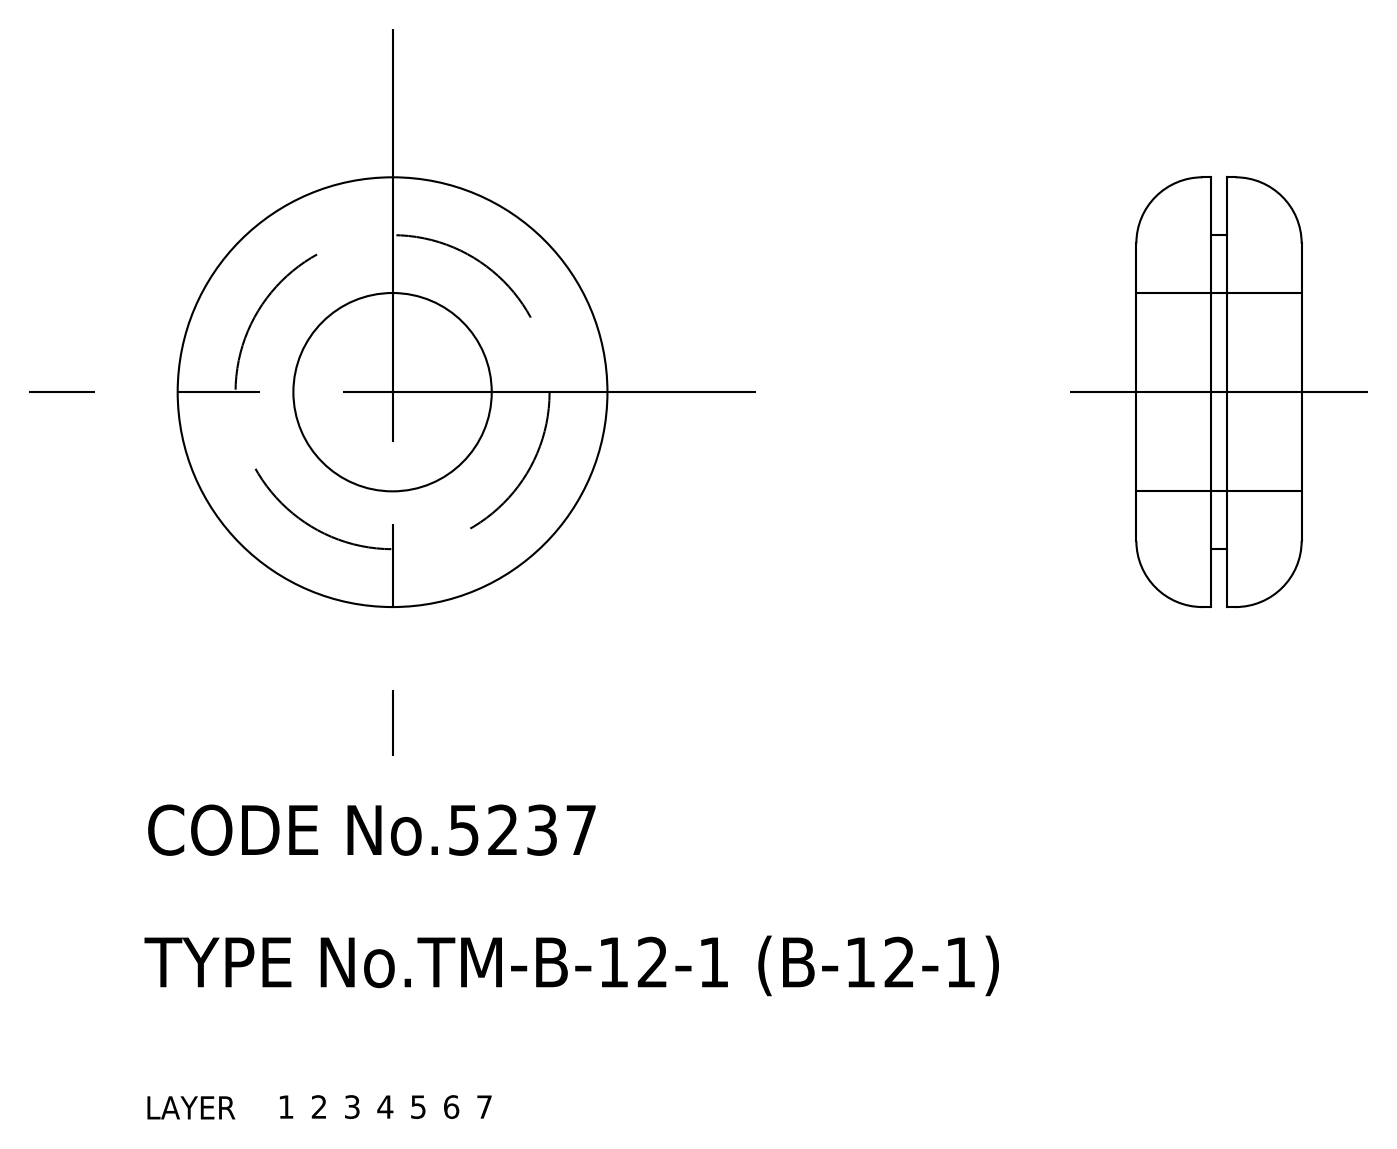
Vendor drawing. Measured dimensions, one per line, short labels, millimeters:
name: grommet
written by: CADfix (AUTOMOTIVE_DESIGN)
unit: mm
bodies: 1 solid, 16 faces (0 planar, 0 cylindrical, 16 other)
size: 26 × 26 × 10
volume: 3 418 mm³; area: 2 209 mm²
